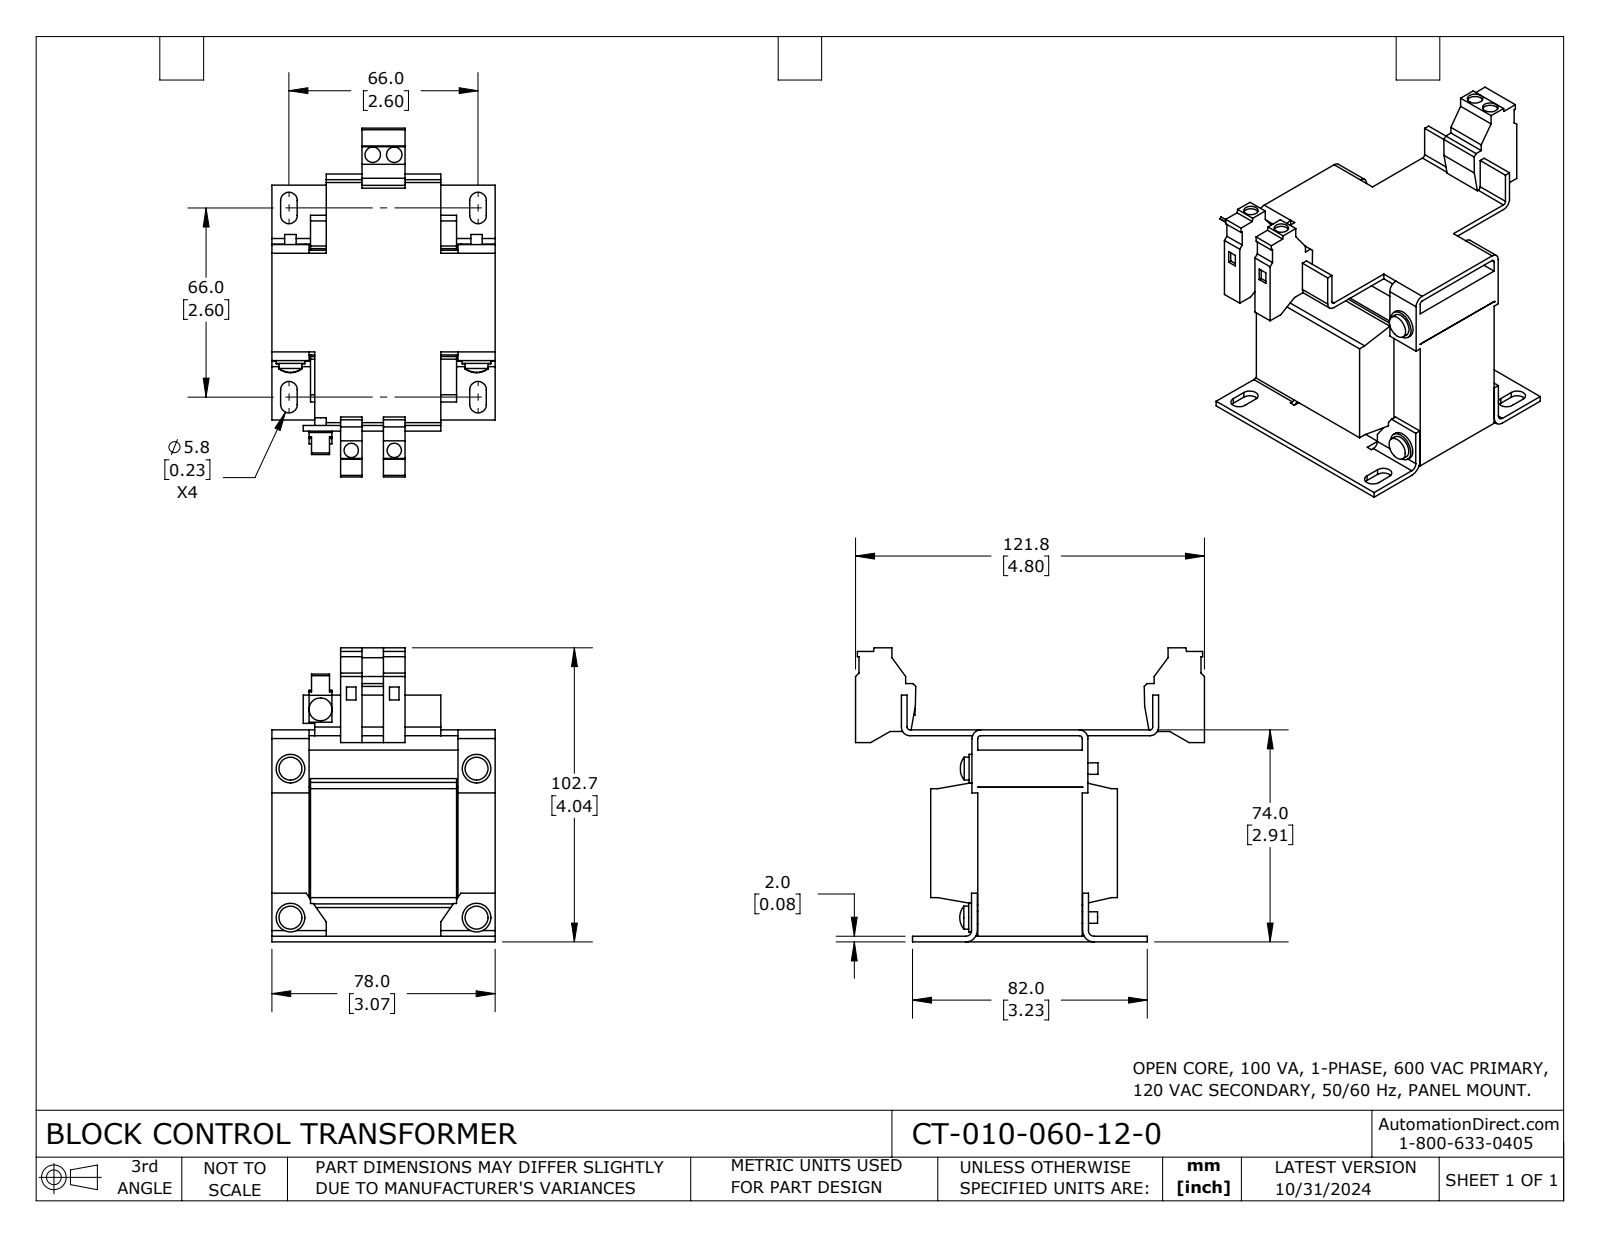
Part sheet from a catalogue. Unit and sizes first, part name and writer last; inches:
Units: inches
Overall size (bounding box): 4.795 × 4.043 × 3.071
Round holes (diameter × count): ⌀0.197 ×2, ⌀0.213 ×2
Round bosses / shafts (diameter × count): ⌀0.315 ×5, ⌀0.157 ×5, ⌀0.394 ×4, ⌀0.177 ×2
Partial cylindrical surfaces — rounded edges, fillets, slot ends (radius × count): R0.114 ×8, R0.039 ×4, R0.118 ×4, R0.079 ×2, R0.157 ×2
Main face-to-face distances: 0.079, 2.835, 0.709, 0.531, 2.047, 0.512, 2.559, 0.02, 2.028, 0.787
Hole centre spacings: 4.074, 0.295, 0.591, 4.063, 4.106
Volume: 17.31 in³ · Surface area: 106.1 in²
Bodies: 1 solid, 334 faces (253 planar, 77 cylindrical, 4 other)
Part name (STEP PRODUCT): CT-010-060-12-0
STEP written by: SolidWorks 2023 (CONFIG_CONTROL_DESIGN)
